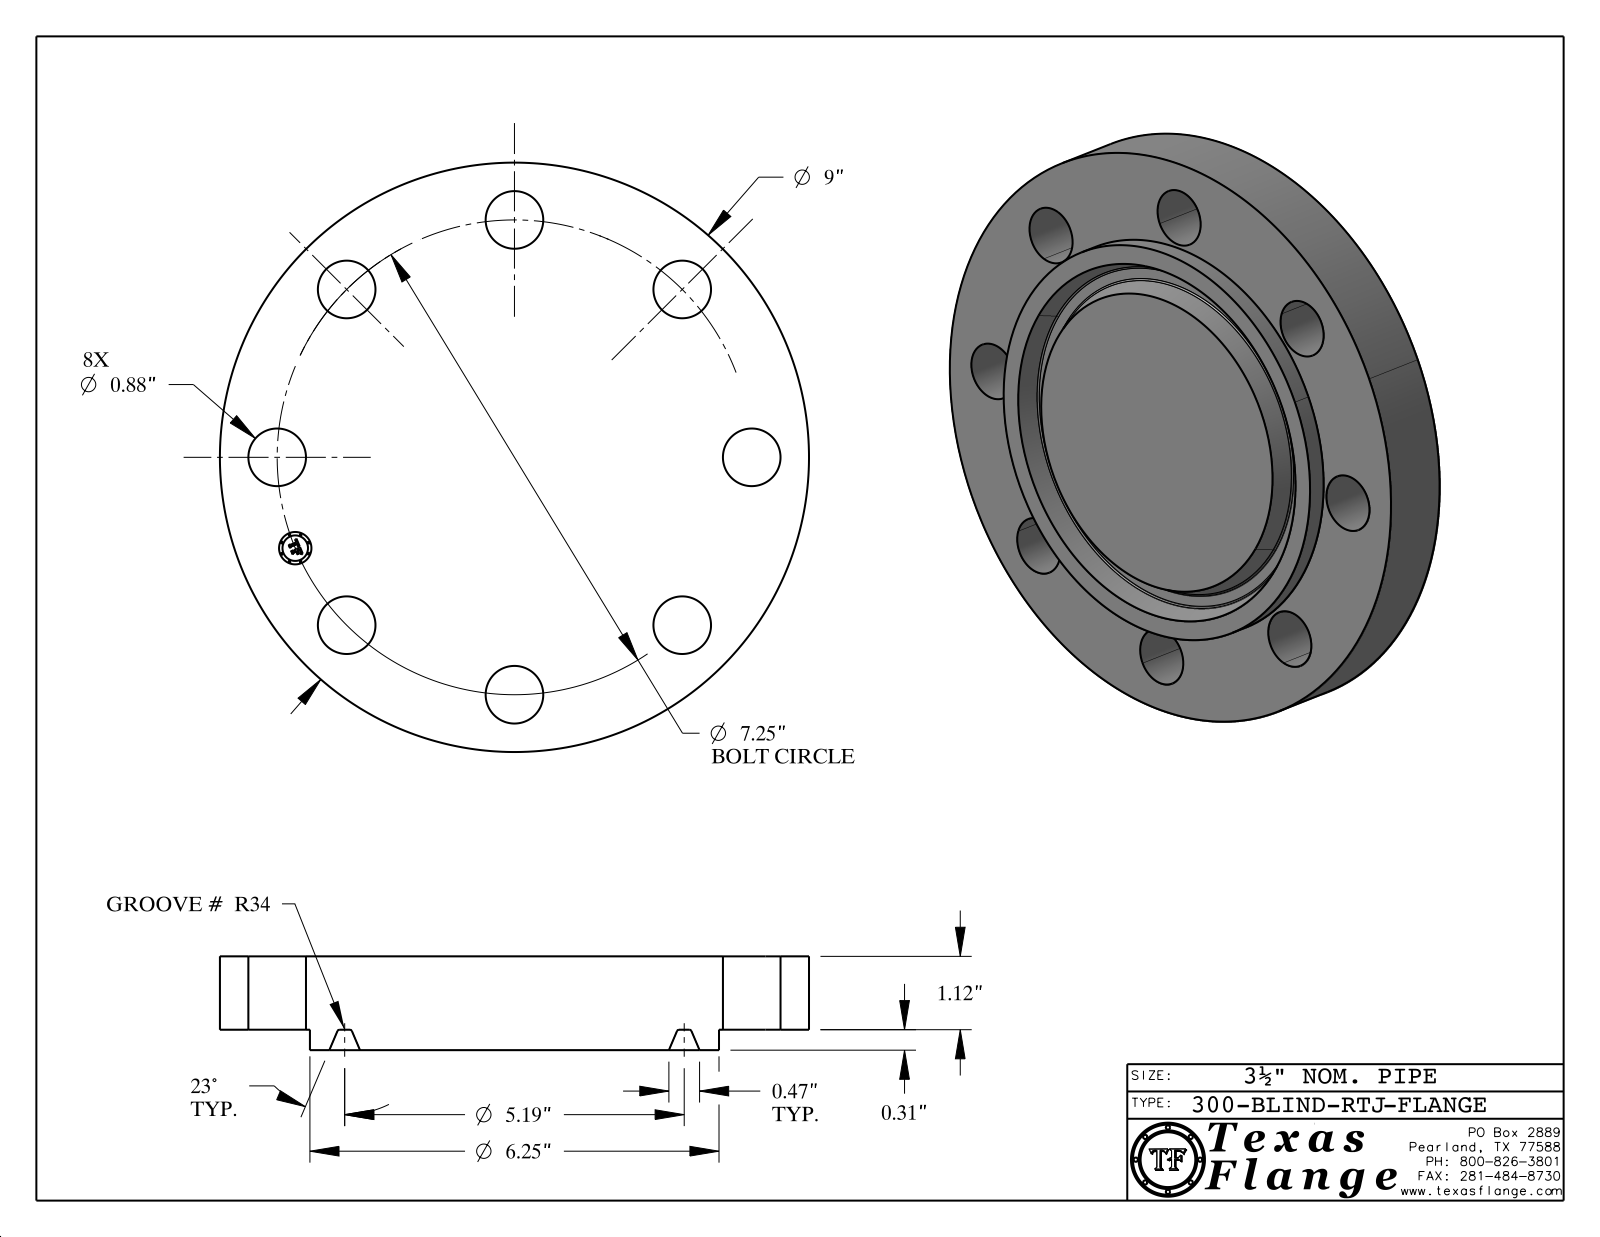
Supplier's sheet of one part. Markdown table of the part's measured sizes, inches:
| quantity | value |
| --- | --- |
| part name | 300-BLIND-RTJ |
| STEP written by | CATIA V5 STEP AP214 (AUTOMOTIVE_DESIGN) |
| units | inches |
| bodies | 1 solid, 418 faces (370 planar, 40 cylindrical, 8 other) |
| overall size | 9 × 9 × 1.433 |
| volume | 73.68 in³ |
| surface area | 186.8 in² |
| round holes (diameter × count) | 0.88 × 8, 0.495 × 1 |
| round bosses / shafts (diameter × count) | 0.03 × 8, 9 × 1, 6.25 × 1, 0.39 × 1 |
| main face-to-face distances | 1.12, 0.313, 1.433, 1.418, 1.105, 0.015, 0.148, 0.144, 0.027, 0.096 |
| hole center spacings | 2.774, 5.127, 6.698, 7.25, 1.415, 7.111, 4.028, 4.028 |
